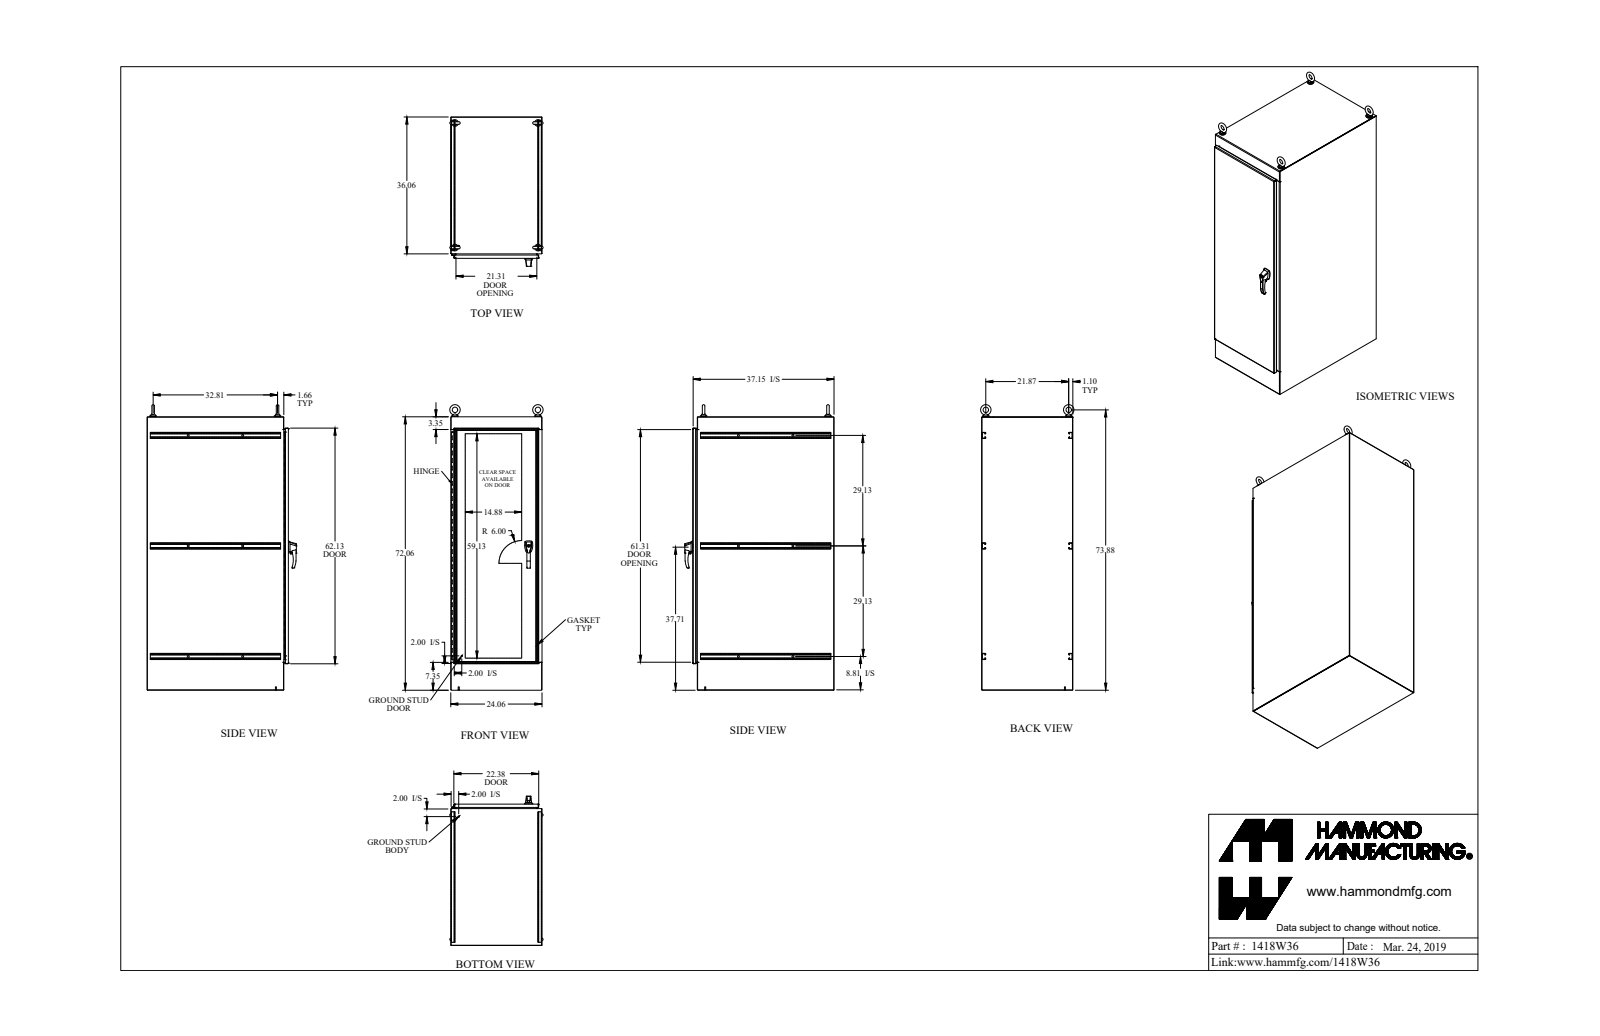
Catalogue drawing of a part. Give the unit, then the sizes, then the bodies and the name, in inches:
Units: inches
Overall size (bounding box): 72.294 × 39.362 × 24.06
Round holes (diameter × count): ⌀0.304 ×10, ⌀0.5 ×6, ⌀0.527 ×4, ⌀0.625 ×4, ⌀0.687 ×4, ⌀0.75 ×4, ⌀0.25 ×2, ⌀0.257 ×2, ⌀0.28 ×2, ⌀0.281 ×2, ⌀0.313 ×2, ⌀0.39 ×2
Round bosses / shafts (diameter × count): ⌀1.75 ×4, ⌀1.5 ×4, ⌀0.281 ×4, ⌀1 ×2, ⌀0.75 ×2, ⌀0.63 ×2, ⌀0.625 ×2, ⌀0.44 ×2
Partial cylindrical surfaces — rounded edges, fillets, slot ends (radius × count): R0.043 ×42, R0.138 ×36, R0.125 ×22, R0.018 ×16, R0.048 ×12, R0.143 ×12, R0.06 ×10, R0.318 ×7
Main face-to-face distances: 0.095, 23.965, 23.87, 37.152, 24.06, 71.965, 37.057, 37.247, 71.87, 72.06
Hole centre spacings: 6, 12, 18, 24, 30, 36, 14.375, 42
Volume: 1 183 in³ · Surface area: 24 983 in²
Bodies: 58 solids, 1738 faces (809 planar, 824 cylindrical, 105 other)
Part name (STEP PRODUCT): 1418W36_Default
STEP written by: SolidWorks 2019 (CONFIG_CONTROL_DESIGN)
